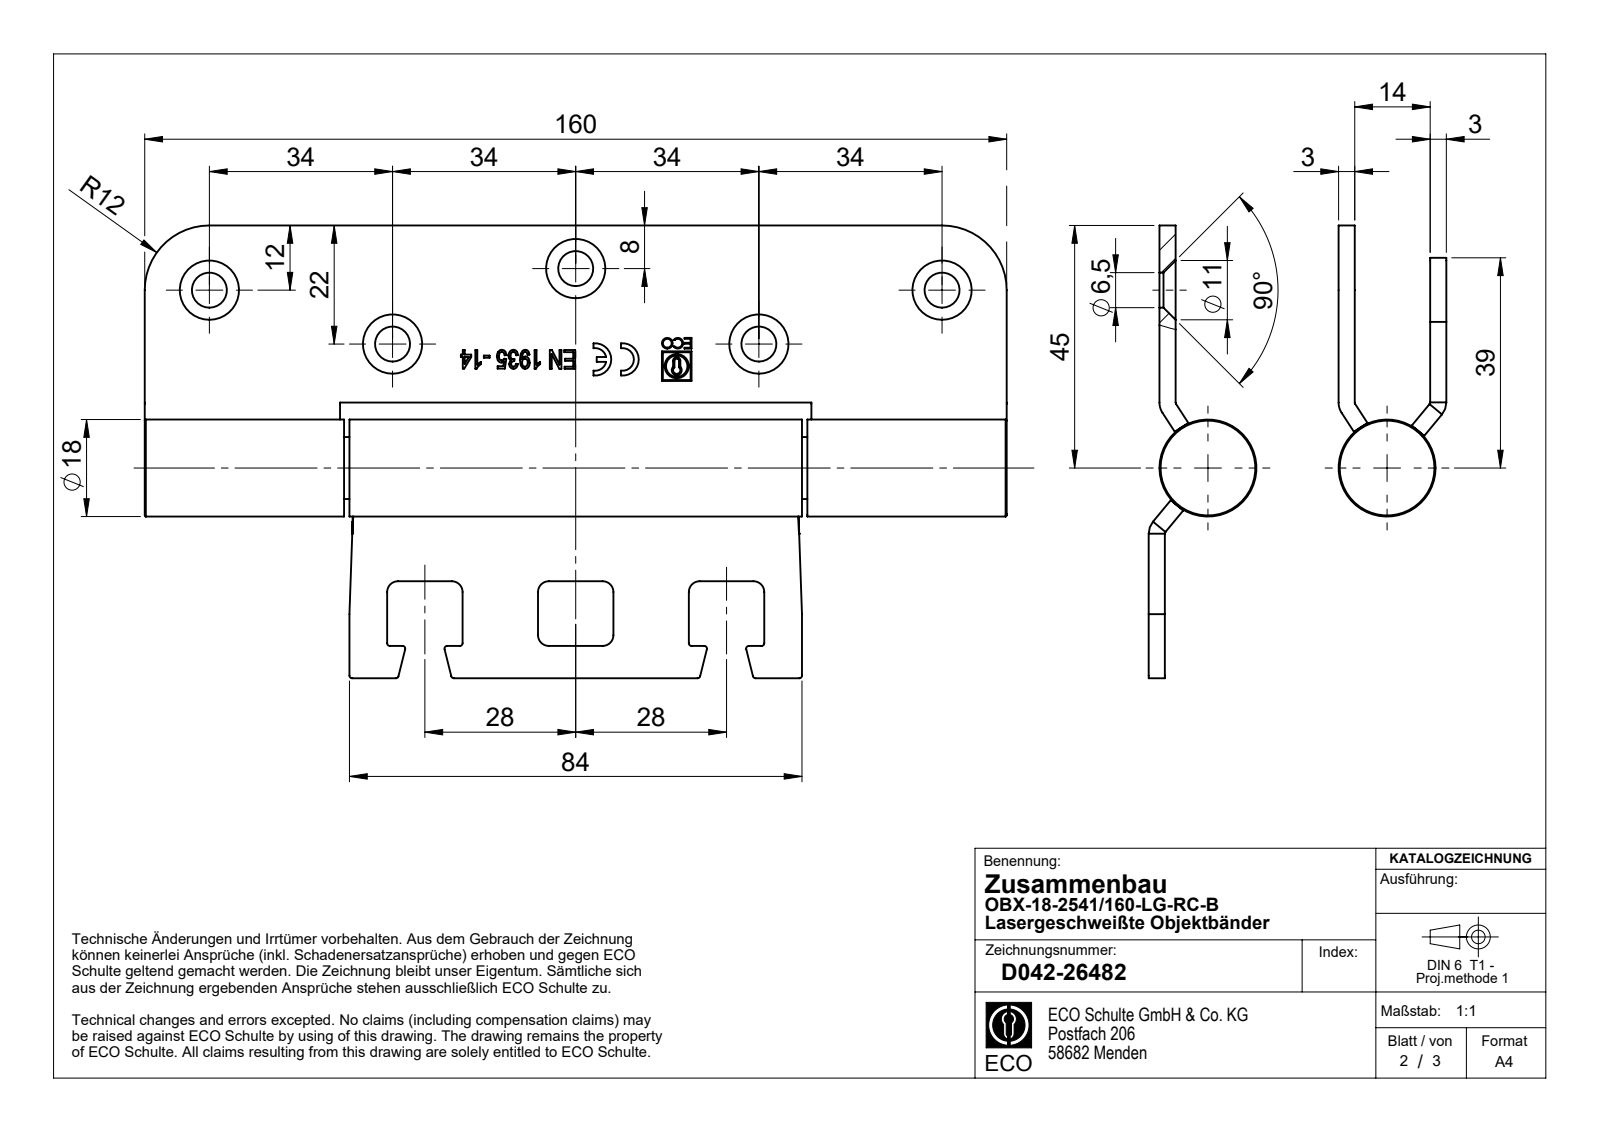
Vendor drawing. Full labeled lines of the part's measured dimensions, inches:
Part name (STEP PRODUCT): D044-14308; DIN5401-III; B01572; D044-14309 (+4 more)
STEP written by: SolidWorks 2017 (AUTOMOTIVE_DESIGN)
Units: inches
Bodies: 11 solids, 456 faces (216 planar, 134 cylindrical, 106 other)
Overall size (bounding box): 6.299 × 2.126 × 0.787
Volume: 3.811 in³ · Surface area: 53.31 in²
Round holes (diameter × count): ⌀0.256 ×5, ⌀0.079 ×2, ⌀0.02 ×1, ⌀0.177 ×1, ⌀0.311 ×1
Round bosses / shafts (diameter × count): ⌀0.709 ×1, ⌀0.472 ×1, ⌀0.465 ×1, ⌀0.453 ×1, ⌀0.303 ×1, ⌀0.157 ×1, ⌀0.065 ×1
Partial cylindrical surfaces — rounded edges, fillets, slot ends (radius × count): R0.02 ×16, R0.079 ×8, R0.01 ×6, R0.027 ×2, R0.083 ×2, R0.118 ×2, R0.138 ×2, R0.472 ×2
Main face-to-face distances: 0.118, 0.669, 0.787, 0.551, 4.803, 1.496, 0.453, 5.846, 1.043, 4.35
Hole centre spacings: 1.395, 1.448, 2.682, 4.035, 0.077, 0.167, 0.181, 0.593
